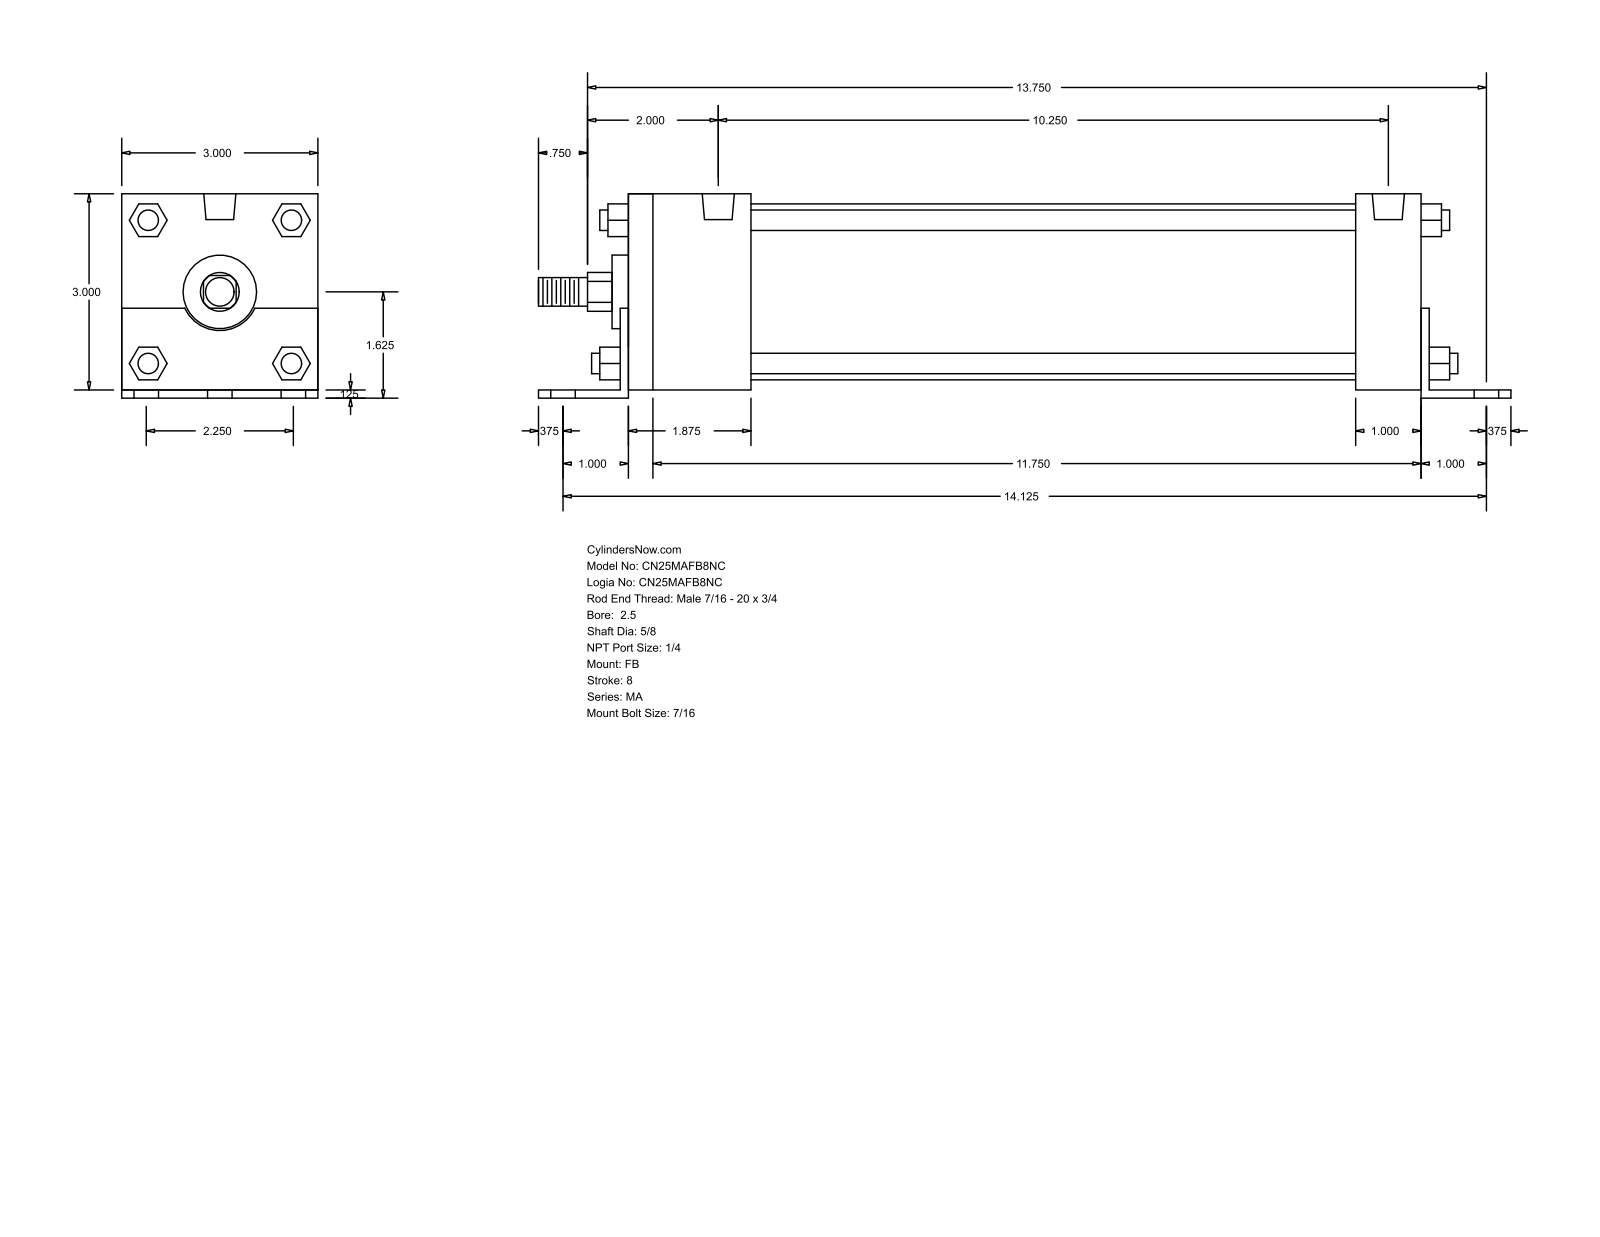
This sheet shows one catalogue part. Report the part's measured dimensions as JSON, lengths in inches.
{"part_name": "MA_FB__0250_0.625", "step_written_by": "GSSL Pune (CONFIG_CONTROL_DESIGN)", "units": "inches", "bodies": {"solids": 0, "faces": 140, "planar": 105, "cylindrical": 35, "other": 0}, "overall_size": [14.875, 3.125, 3], "round_holes": [[0.437, 6], [0.313, 4], [0.492, 2]], "round_bosses_or_shafts": [[0.313, 4], [2.69, 1], [1.125, 1], [0.625, 1], [0.437, 1]], "partial_cylinders_radius": [[0.297, 1], [0.593, 1]], "face_to_face_distances": [3, 0.125, 3.125, 12.125, 12.375, 0.125, 12.25, 1.875, 1, 12.25], "hole_center_spacings": [1.125, 14.17, 14.125, 1.875, 2.25, 2.628, 10.25, 11.804]}
